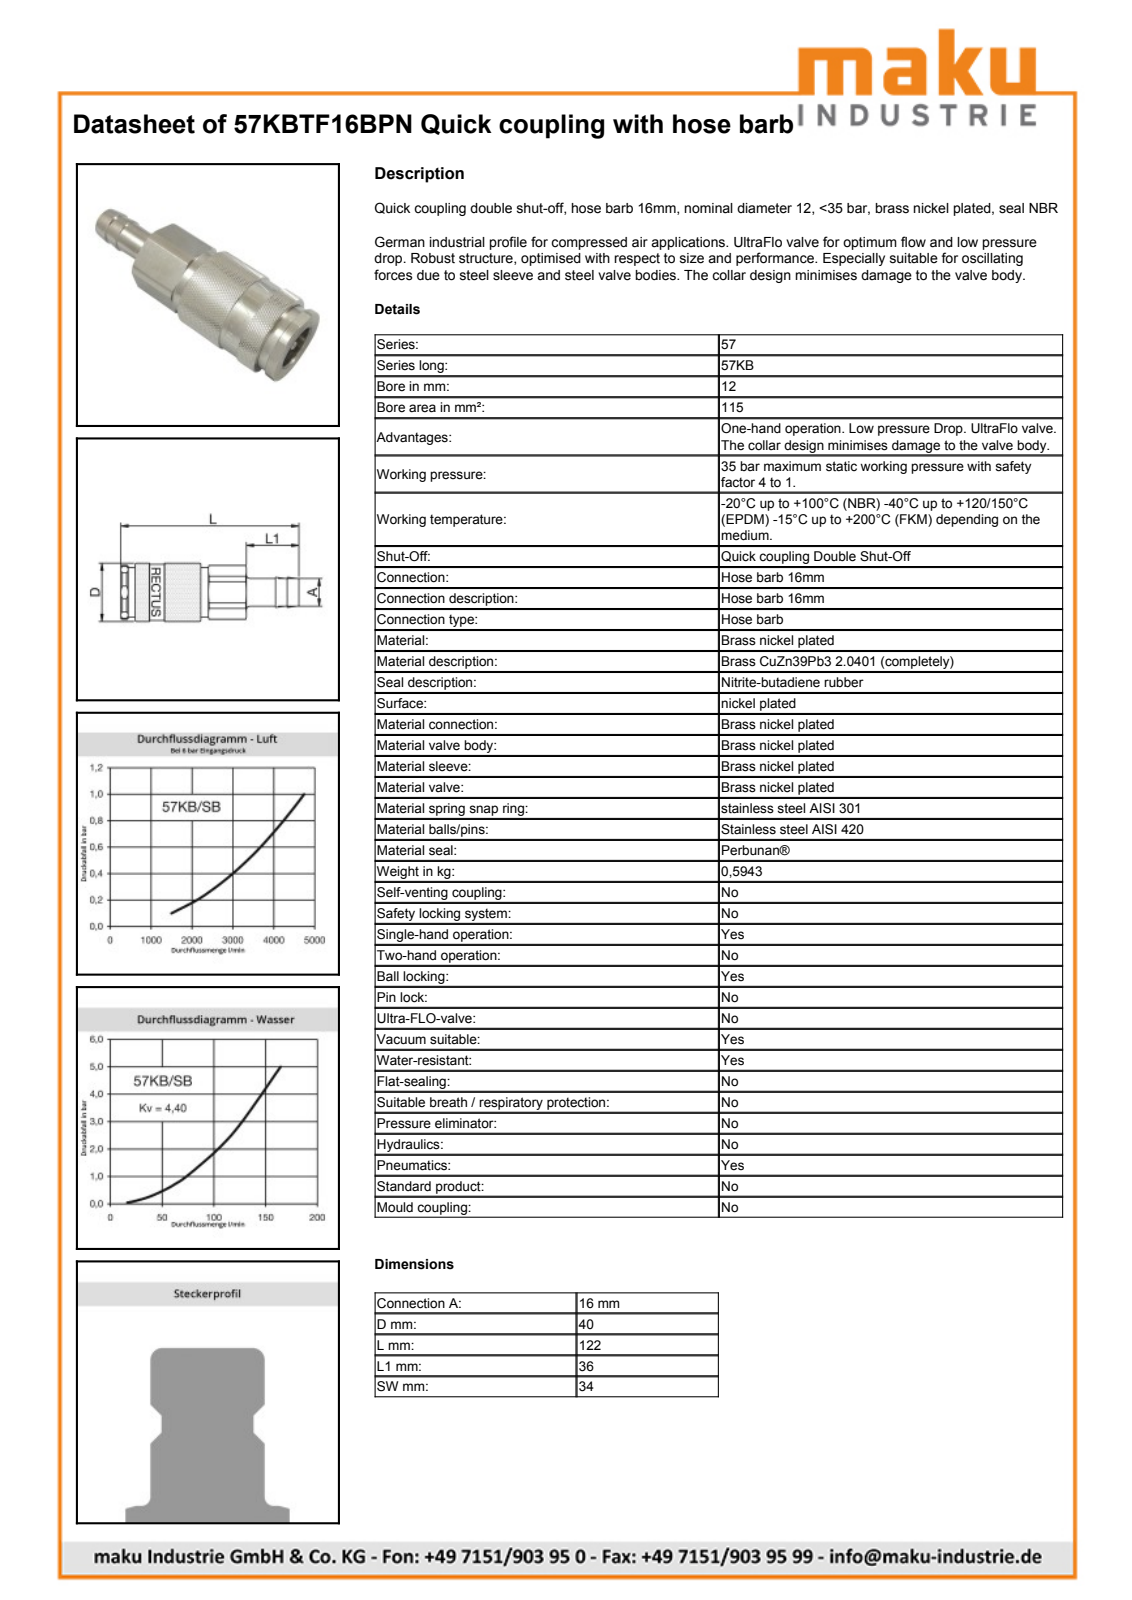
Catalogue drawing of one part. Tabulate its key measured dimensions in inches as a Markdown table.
| quantity | value |
| --- | --- |
| part name | D107025 |
| STEP written by | Autodesk Inventor 2013 (AUTOMOTIVE_DESIGN) |
| units | inches |
| bodies | 2 solids, 510 faces (196 planar, 71 cylindrical, 243 other) |
| overall size | 4.805 × 1.575 × 1.575 |
| volume | 6.01 in³ |
| surface area | 40.3 in² |
| round holes (diameter × count) | 1.181 × 1, 1.189 × 1, 1.346 × 1, 1.362 × 1 |
| round bosses / shafts (diameter × count) | 1.575 × 1, 1.516 × 1, 1.339 × 1, 1.134 × 1, 1.118 × 1, 1.067 × 1, 0.632 × 1 |
| partial cylindrical surfaces (radius × count) | 0.728 × 1, 0.754 × 1 |
| main face-to-face distances | 1.339, 3.388, 1.338, 1.417, 1.488, 1.9, 0.63, 0.346, 1.142, 3.041 |
